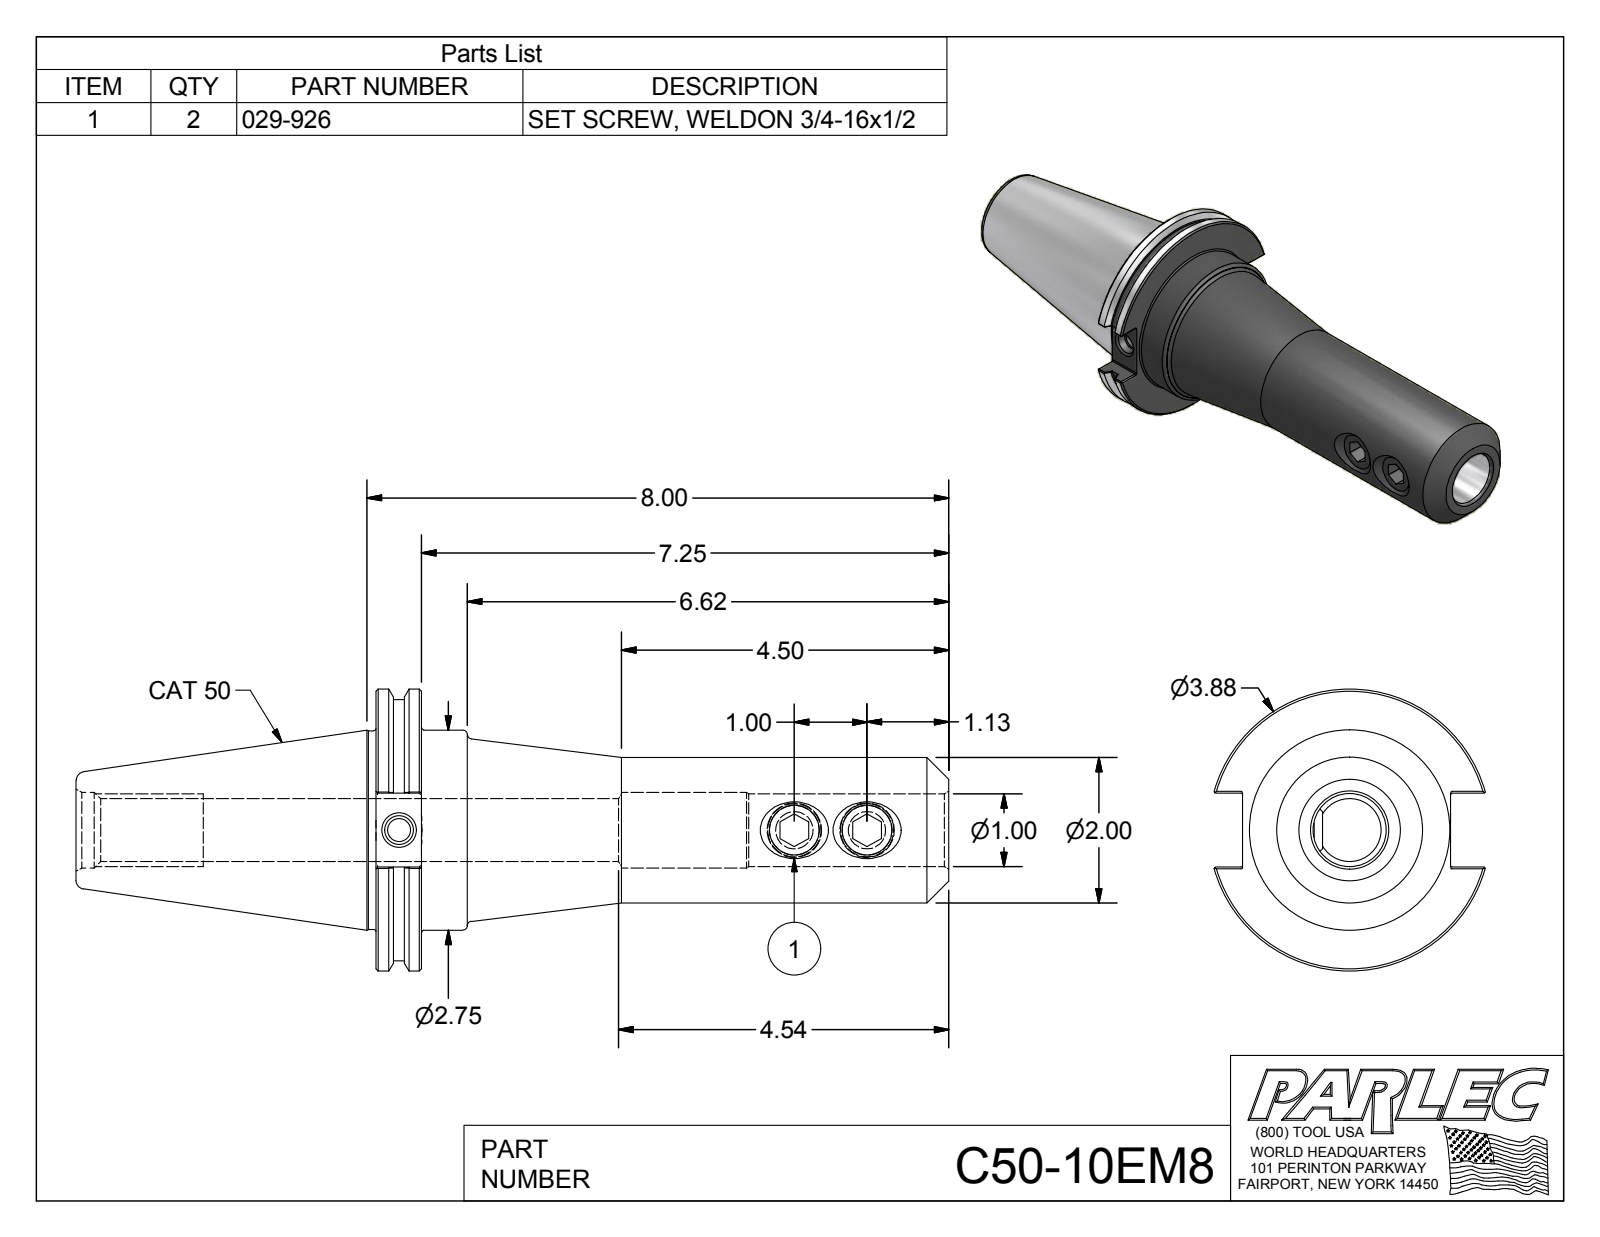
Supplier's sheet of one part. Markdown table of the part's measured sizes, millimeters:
| quantity | value |
| --- | --- |
| part name | C50-10EM8; C50-10EM8-1; 029-926 |
| STEP written by | Autodesk Inventor 2012 (AUTOMOTIVE_DESIGN) |
| units | millimeters |
| bodies | 3 solids, 120 faces (51 planar, 31 cylindrical, 38 other) |
| overall size | 304.8 × 98.4 × 94.7 |
| volume | 658 100 mm³ |
| surface area | 90 770 mm² |
| round holes (diameter × count) | 17.3 × 2, 8 × 1, 10.1 × 1, 22 × 1, 25.4 × 1, 26.4 × 1, 26.4 × 1 |
| round bosses / shafts (diameter × count) | 19.1 × 2, 98.4 × 1, 91.3 × 1, 69.9 × 1, 69.3 × 1, 50.8 × 1 |
| partial cylindrical surfaces (radius × count) | 0.5 × 12 |
| main face-to-face distances | 15.9, 12.7, 10, 200, 184.2, 57.4, 104.8, 120.7, 304.8, 72.6 |
| hole center spacings | 25.4, 138, 163.4 |
